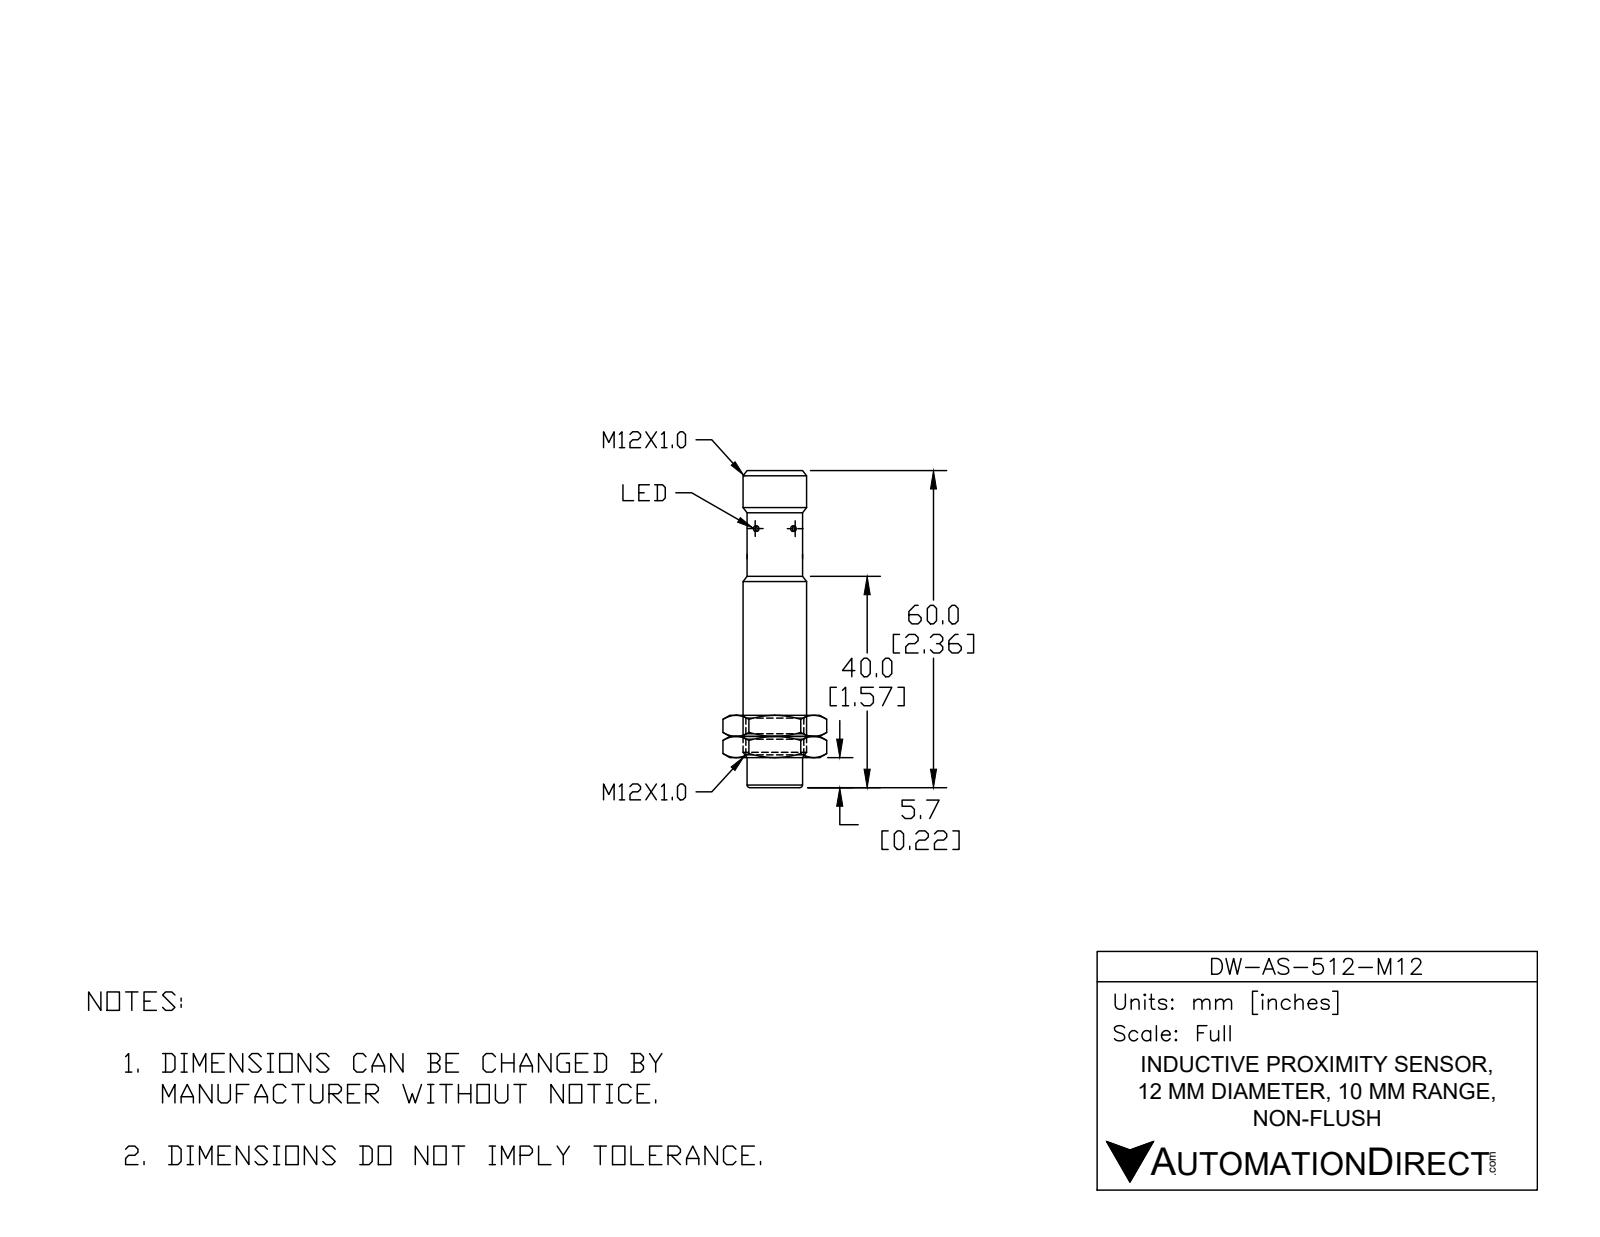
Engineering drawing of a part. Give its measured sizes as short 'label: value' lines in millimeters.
name: DW-AS-512-M12
written by: SolidWorks 2021 (AUTOMOTIVE_DESIGN)
unit: mm
bodies: 3 solids, 65 faces (18 planar, 10 cylindrical, 37 other)
size: 60 × 19.6 × 17
volume: 7 470 mm³; area: 3 663 mm²
holes: 2× ⌀1, 1× ⌀10.9
bosses: 1× ⌀12, 1× ⌀10.5
face distances: 4, 8, 17, 12, 34.3, 38.3, 42.3, 46.3, 60, 25.7
